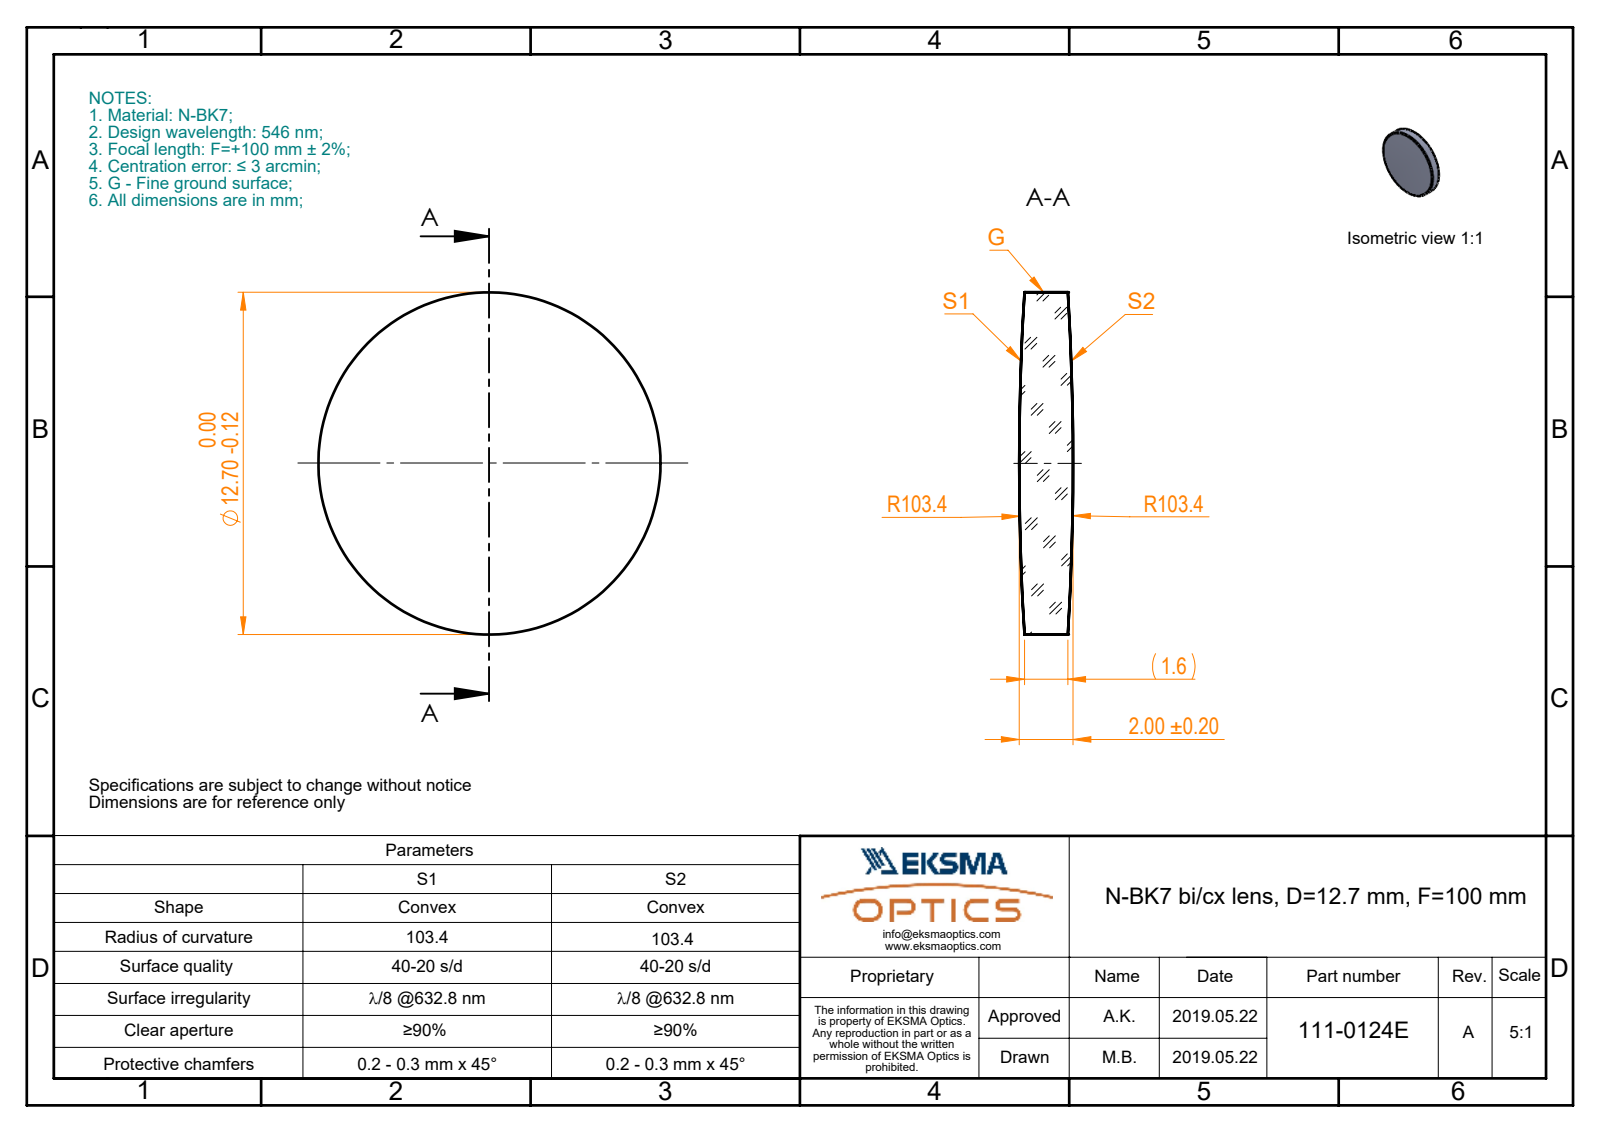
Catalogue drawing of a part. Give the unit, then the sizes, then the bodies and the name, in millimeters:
Units: millimetres
Overall size (bounding box): 12.7 × 12.7 × 2
Round bosses / shafts (diameter × count): ⌀12.7 ×1
Volume: 229 mm³ · Surface area: 318 mm²
Bodies: 1 solid, 6 faces (0 planar, 2 cylindrical, 4 other)
Part name (STEP PRODUCT): 111-0124E BK7 bi-cx 12.7 F100
STEP written by: SolidWorks 2017 (CONFIG_CONTROL_DESIGN)
